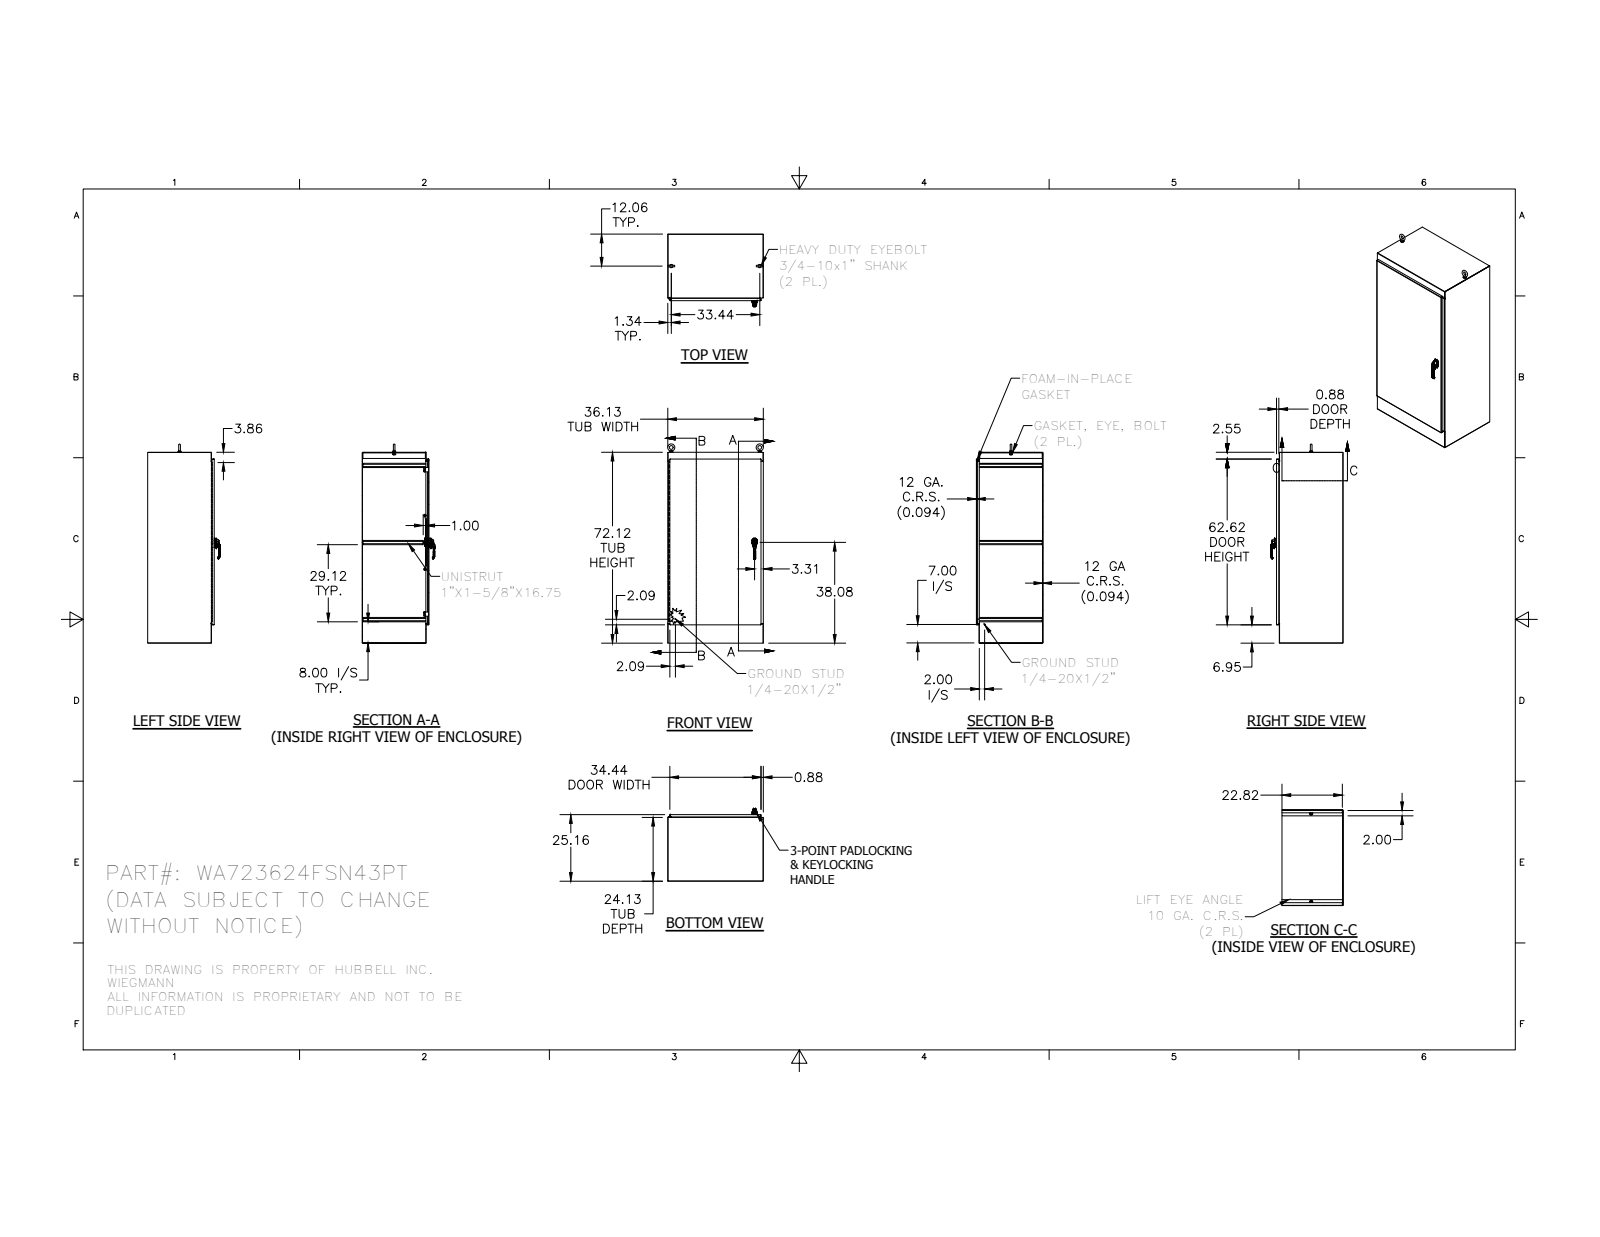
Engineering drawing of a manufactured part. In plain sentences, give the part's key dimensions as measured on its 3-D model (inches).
The part is named "LOCK-NUT_AF0; HFW3025; HFW31233; 7379-M6-8X25_AF0 (+8 more)". Its 3-D file was written by "SolidWorks 2014 (AUTOMOTIVE_DESIGN)". It is 52 solids with 1938 faces: 834 planar, 782 cylindrical and 322 other. Overall it measures 75.248 by 36.125 by 25.16 inches. Its volume is 1 173 cubic inches and its surface area 24 298 square inches. Round holes: 8 of diameter 0.277, 4 of diameter 0.2, 3 of diameter 0.28, 2 of diameter 0.241, 2 of diameter 0.25, 2 of diameter 0.252, 2 of diameter 0.4, 2 of diameter 0.407, 2 of diameter 0.45, 2 of diameter 0.642, 2 of diameter 0.813, 1 of diameter 0.125. Round bosses or shafts: 3 of diameter 0.25, 2 of diameter 1.25, 2 of diameter 1.12, 2 of diameter 1, 2 of diameter 0.75, 2 of diameter 0.563, 2 of diameter 0.527, 2 of diameter 0.5. Partial cylindrical surfaces (rounded edges, fillets, slot ends): 16 of radius 0.01, 16 of radius 0.031, 14 of radius 0.05, 14 of radius 0.125, 12 of radius 0.019, 12 of radius 0.053, 12 of radius 0.086, 12 of radius 0.125. The main face-to-face distances are 0.094, 25.067, 36.031, 24.973, 25.161, 35.938, 72.031, 36.125, 24.031, 1.035. The hole center spacings are 54.196, 54.946, 0.762, 0.764, 1.195, 1.271, 54.561, 54.571.
